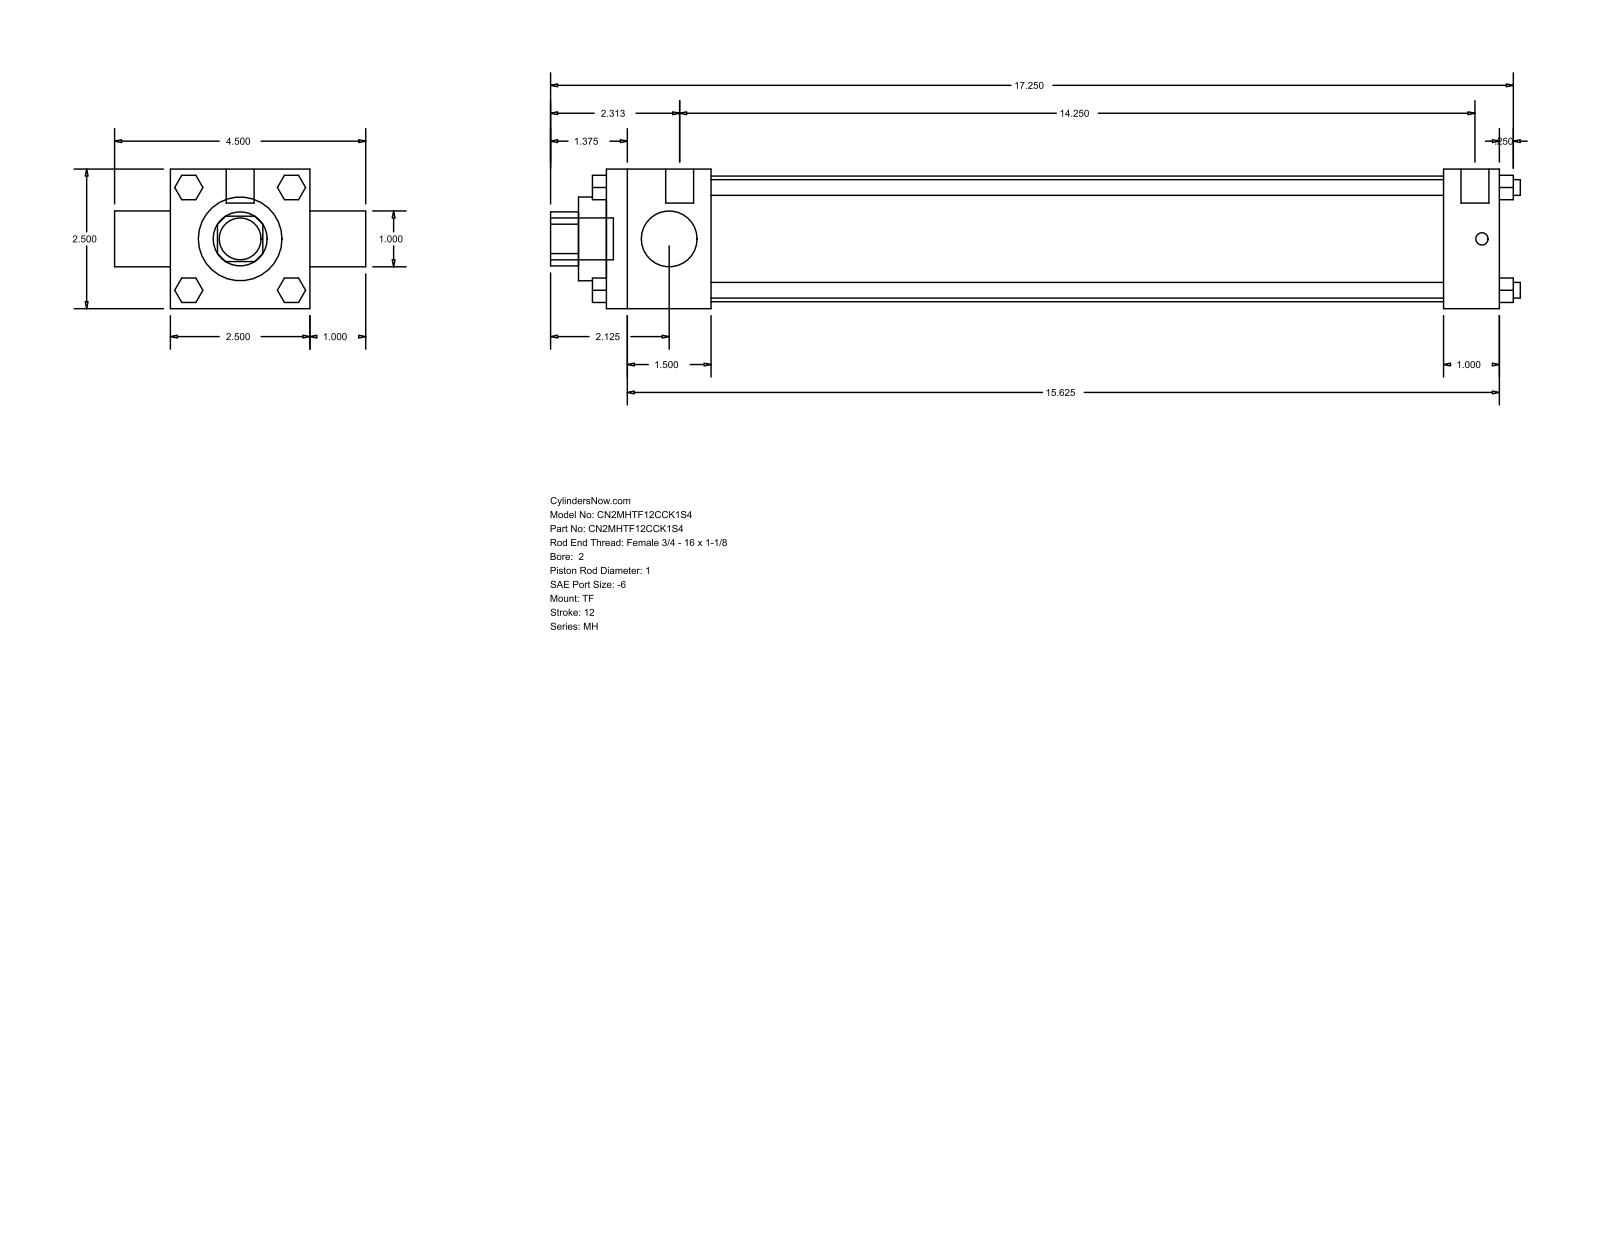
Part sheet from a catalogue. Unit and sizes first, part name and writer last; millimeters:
Units: millimetres
Overall size (bounding box): 441.32 × 114.3 × 63.5
Round holes (diameter × count): ⌀25.4 ×2, ⌀38.1 ×1, ⌀57.15 ×1
Round bosses / shafts (diameter × count): ⌀7.14 ×4, ⌀5.56 ×3, ⌀12.7 ×2, ⌀19.05 ×1
Partial cylindrical surfaces — rounded edges, fillets, slot ends (radius × count): R12.29 ×1
Main face-to-face distances: 63.5, 406.4, 25.4, 47.63, 381, 333.37, 358.77, 88.9, 419.1, 6.35
Bodies: 0 solids, 120 faces (92 planar, 28 cylindrical, 0 other)
Part name (STEP PRODUCT): MH_TF__0200_1
STEP written by: GSSL Pune (CONFIG_CONTROL_DESIGN)
